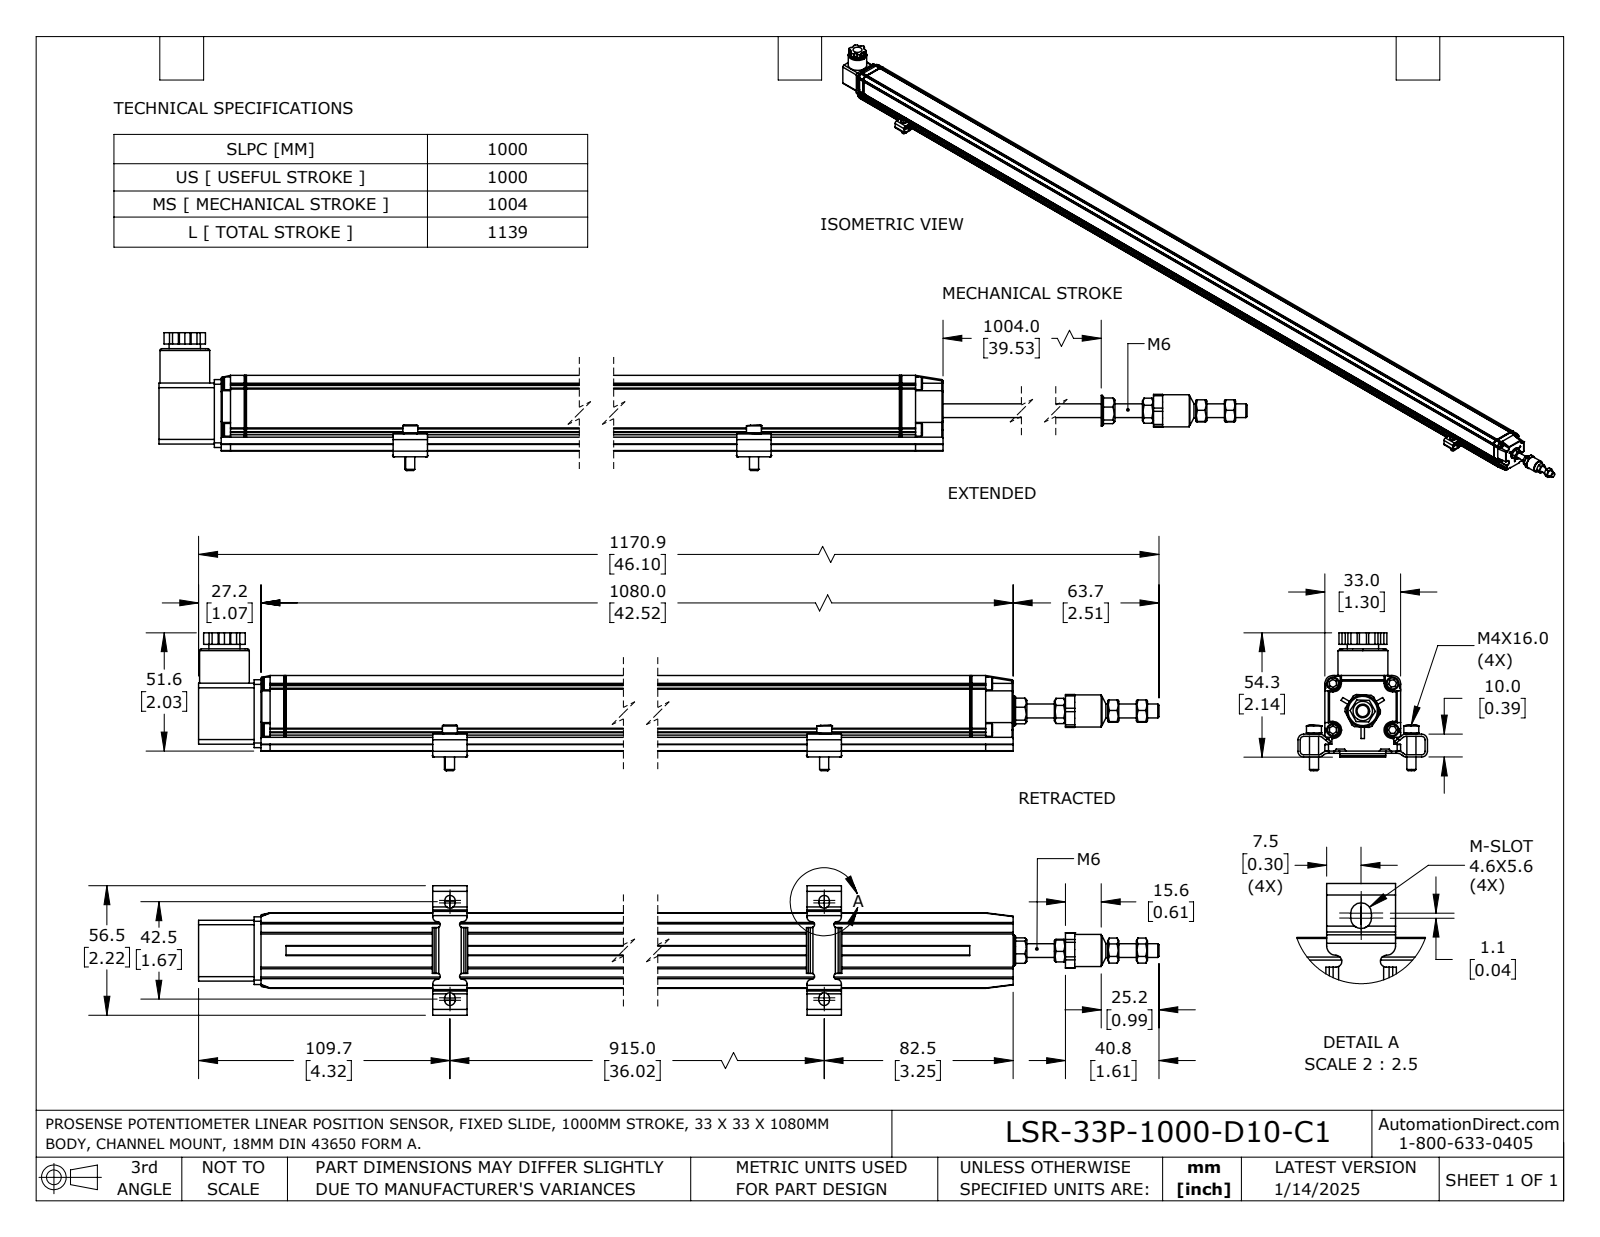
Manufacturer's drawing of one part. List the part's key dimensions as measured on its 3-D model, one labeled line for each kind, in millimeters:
Part name (STEP PRODUCT): LSR-33P-1000-D10-C1
STEP written by: SolidWorks 2023 (AUTOMOTIVE_DESIGN)
Units: millimetres
Bodies: 14 solids, 995 faces (641 planar, 269 cylindrical, 85 other)
Overall size (bounding box): 1170.8 × 60.2 × 56.5
Volume: 1 076 000 mm³ · Surface area: 247 800 mm²
Round holes (diameter × count): ⌀2.7 ×4, ⌀3.3 ×4, ⌀4.3 ×1, ⌀5.2 ×1, ⌀5.3 ×1, ⌀5.9 ×1, ⌀7 ×1, ⌀7.2 ×1, ⌀10 ×1, ⌀10.5 ×1, ⌀14.6 ×1, ⌀15.3 ×1
Round bosses / shafts (diameter × count): ⌀4 ×5, ⌀3 ×5, ⌀6.5 ×4, ⌀5.6 ×4, ⌀21.7 ×1, ⌀14 ×1, ⌀13.6 ×1, ⌀13.4 ×1
Partial cylindrical surfaces — rounded edges, fillets, slot ends (radius × count): R2 ×28, R0.5 ×23, R0.2 ×16, R1.3 ×8, R1.5 ×8, R2.3 ×8, R3 ×8, R1 ×4
Main face-to-face distances: 33, 3, 5.6, 30, 27.4, 2, 1, 3.6, 31, 4.7
Hole centre spacings: 1.2, 14.8, 15.4, 17.7, 18.5, 20.3, 26, 33
